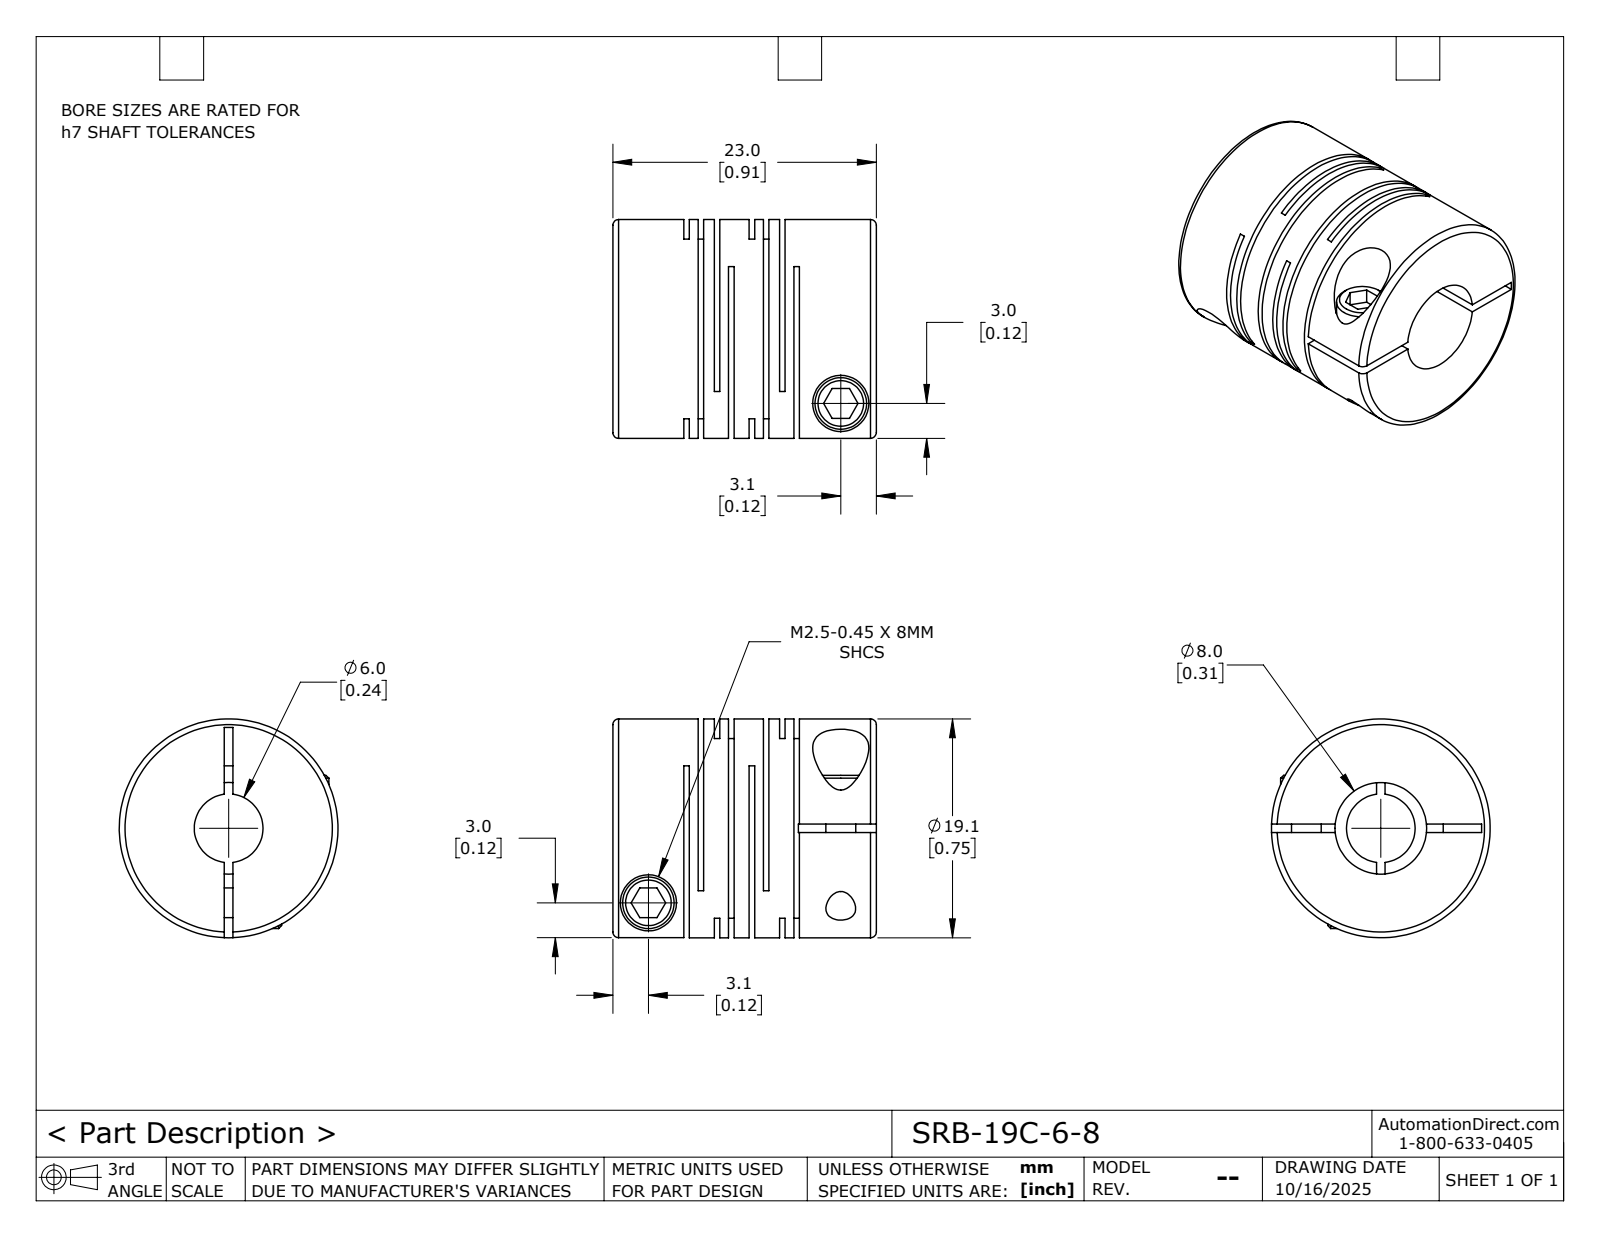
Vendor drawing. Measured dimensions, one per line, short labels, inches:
name: SRB-19C-6-8
written by: SolidWorks 2024 (CONFIG_CONTROL_DESIGN)
unit: in
bodies: 1 solid, 115 faces (60 planar, 42 cylindrical, 13 other)
size: 0.906 × 0.752 × 0.752
volume: 0.281 in³; area: 8.866 in²
holes: 2× ⌀0.102, 2× ⌀0.193, 1× ⌀0.236, 1× ⌀0.315
bosses: 2× ⌀0.177, 1× ⌀0.752
face distances: 0.104, 0.019, 0.224, 0.049, 0.085, 0.12, 0.206, 0.03, 0.175, 0.055
